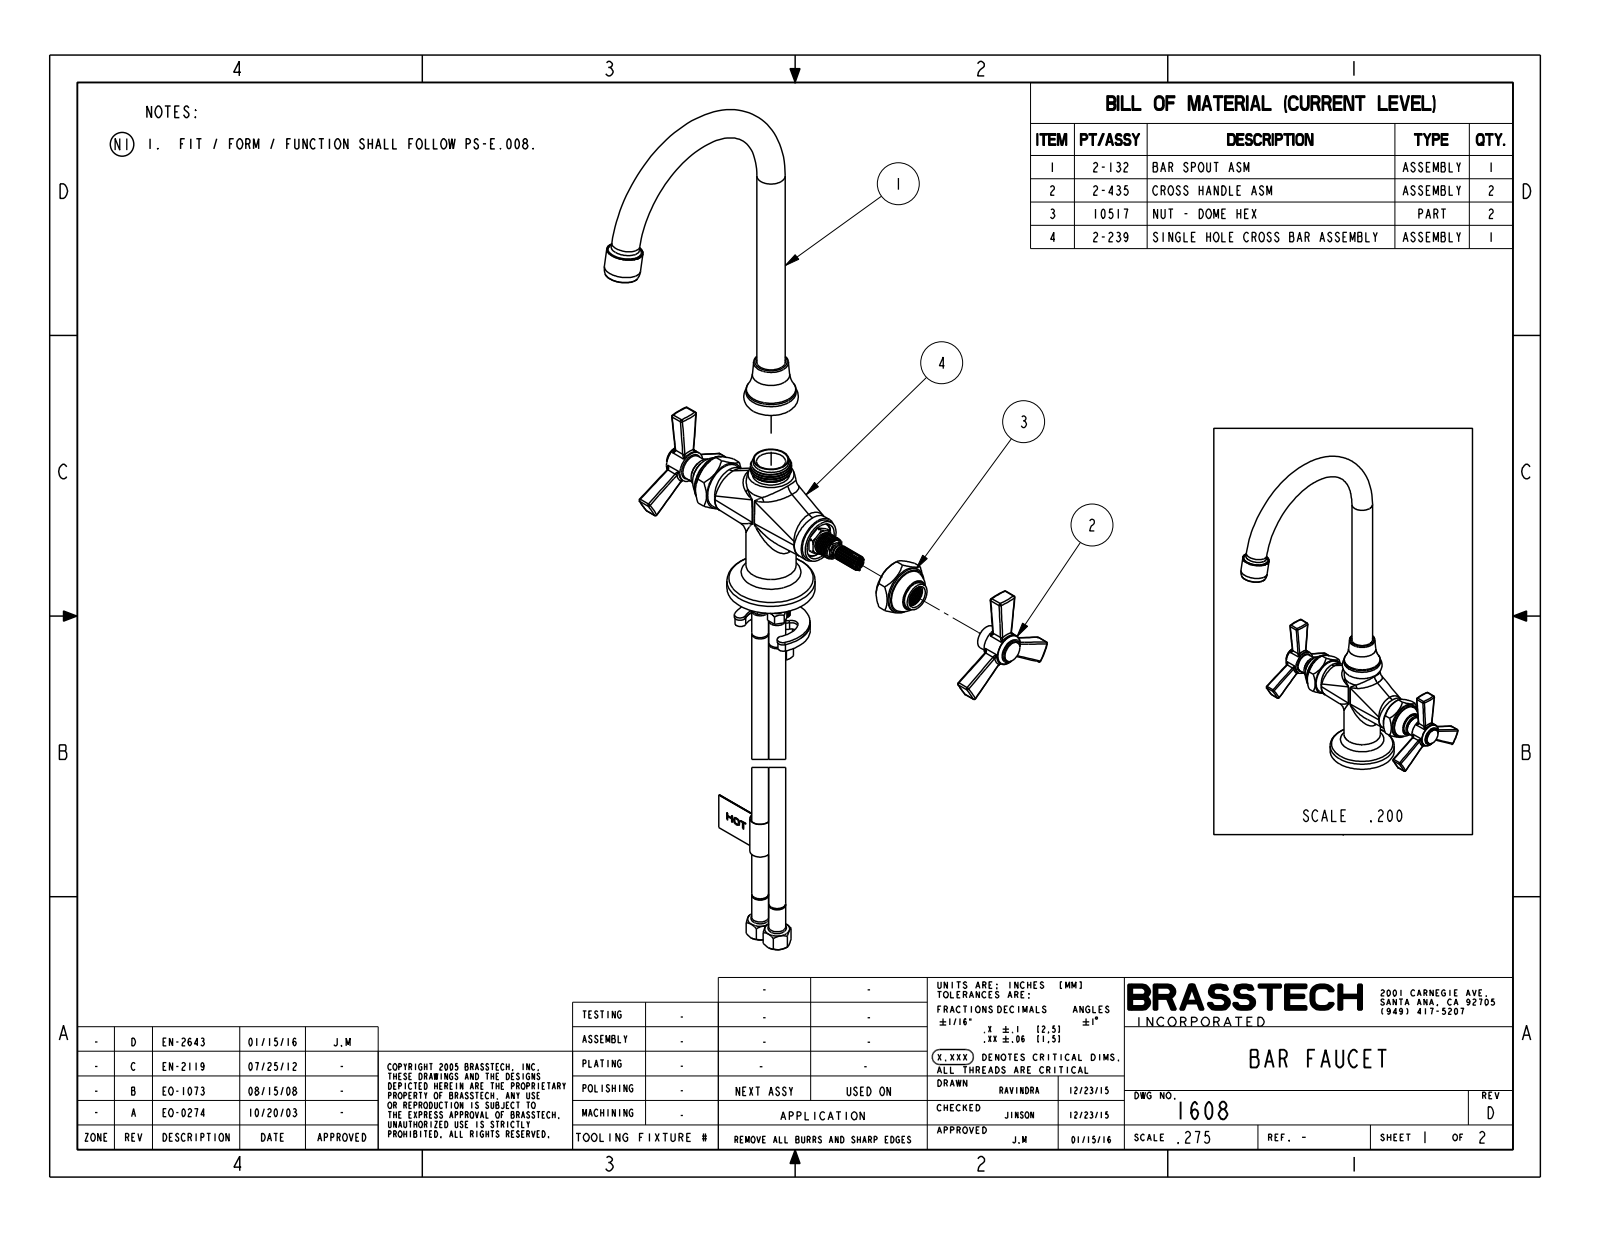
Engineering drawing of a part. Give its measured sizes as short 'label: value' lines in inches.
name: 1608_WEB
written by: PRO/ENGINEER BY PARAMETRIC TECHNOLOGY CORPORATION, 2009300 (CONFIG_CONTROL_DESIGN)
unit: in
bodies: 0 solids, 346 faces (52 planar, 60 cylindrical, 234 other)
size: 13.31 × 7.119 × 6.836
bosses: 2× ⌀0.706, 1× ⌀2.2, 1× ⌀1.25, 1× ⌀1.248, 1× ⌀1.215, 1× ⌀1.17, 1× ⌀0.909, 1× ⌀0.8
rounds: 6× R0.04, 6× R0.1
face distances: 0.47, 3.77, 3.48, 3.3, 4.24, 0.475, 1.173, 1.643, 4.943, 5.413
